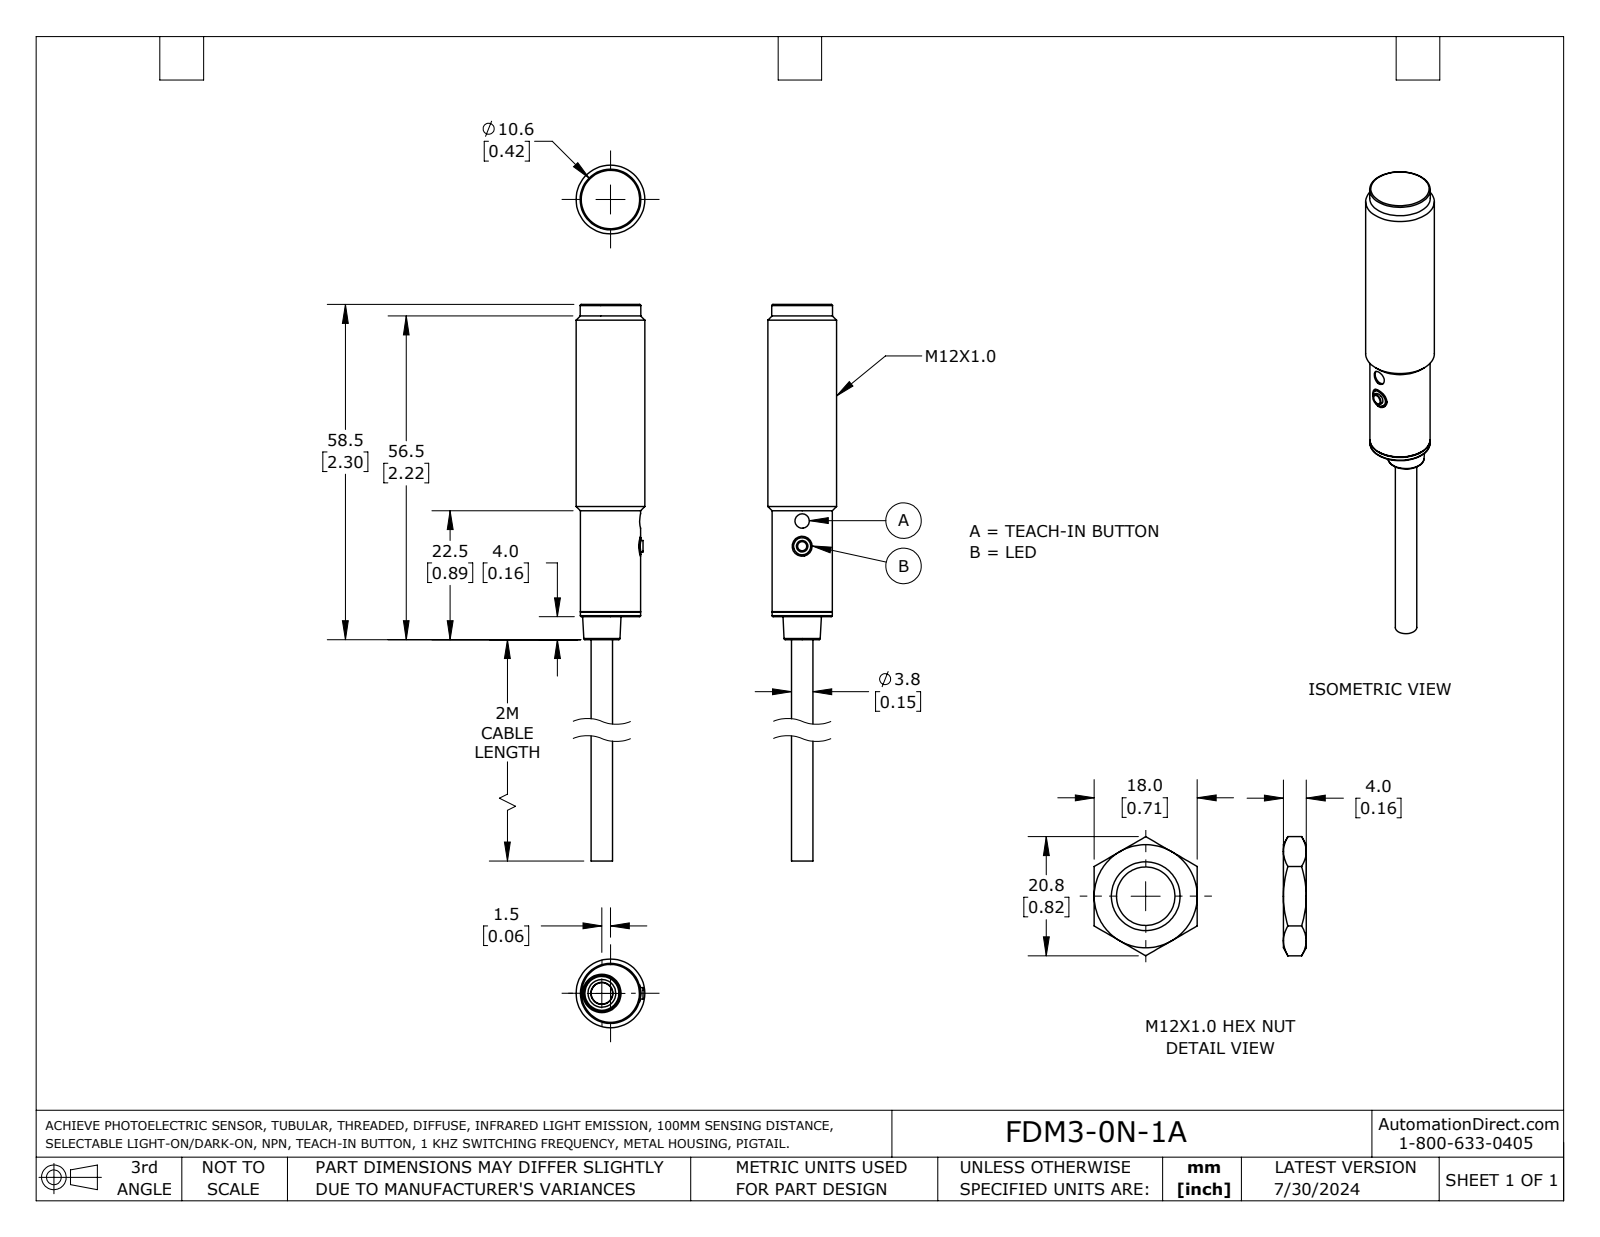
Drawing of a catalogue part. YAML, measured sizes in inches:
part_name: "DM3_1A_fig"
step_written_by: "SolidWorks 2023 (AUTOMOTIVE_DESIGN)"
units: inches
bodies: {solids: 1, faces: 30, planar: 9, cylindrical: 12, other: 9}
overall_size: [3.72, 0.472, 0.472]
volume: 0.374
surface_area: 4.276
round_holes:
  - {diameter: 0.098, count: 1}
  - {diameter: 0.138, count: 1}
  - {diameter: 0.152, count: 1}
round_bosses_or_shafts:
  - {diameter: 0.472, count: 1}
  - {diameter: 0.417, count: 1}
  - {diameter: 0.413, count: 1}
  - {diameter: 0.148, count: 1}
  - {diameter: 0.118, count: 1}
  - {diameter: 0.079, count: 1}
partial_cylinders:
  - {radius: 0.193, count: 1}
face_to_face_distances: [2.146, 1.575, 3.72, 1.417, 0.157, 2.303, 0.031, 1.606, 0.189, 2.114]
hole_center_spacings: [0.173]
